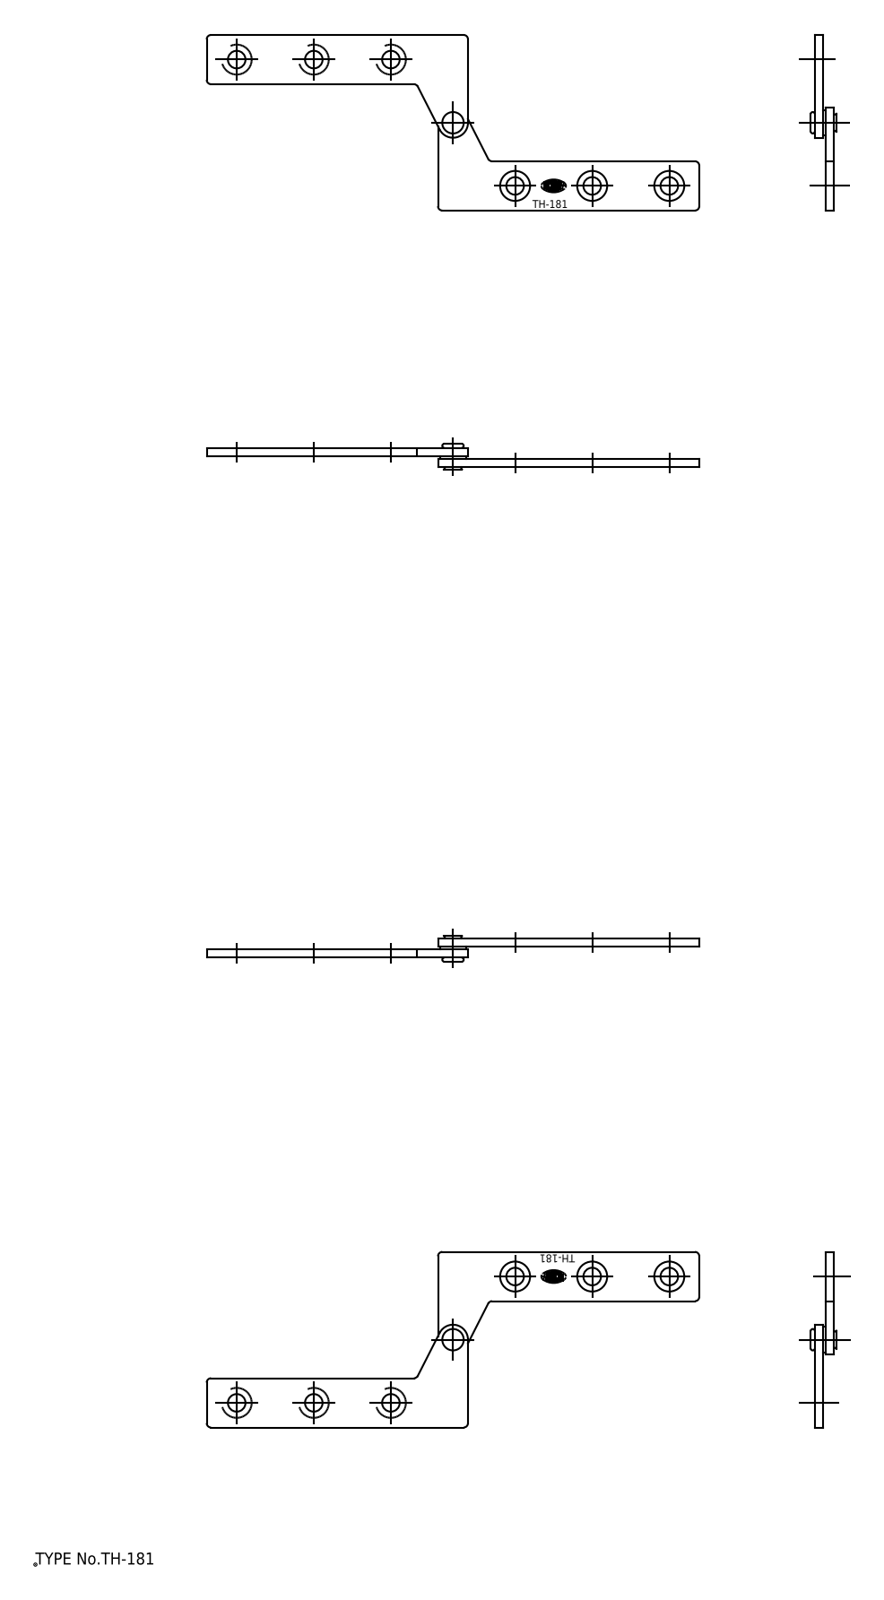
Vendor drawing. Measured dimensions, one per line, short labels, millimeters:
name: シャフト(右下・左上用）; ヒンジピース(A); ワッシャー（右下・左上用）; ヒンジピース(B) (+4 more)
written by: spGate 16.7.1 (AUTOMOTIVE_DESIGN)
unit: mm
bodies: 8 solids, 130 faces (38 planar, 64 cylindrical, 28 other)
size: 67 × 61 × 24
volume: 6 007 mm³; area: 7 968 mm²
holes: 3× ⌀4.1, 1× ⌀3.2
bosses: 1× ⌀6, 1× ⌀3
rounds: 4× R1, 1× R3.5
face distances: 60.5, 2.5, 2, 4.5, 58, 0.5, 62.5, 63, 58.5, 61
hole spacings: 18, 20.68, 35.69, 36, 52.61
